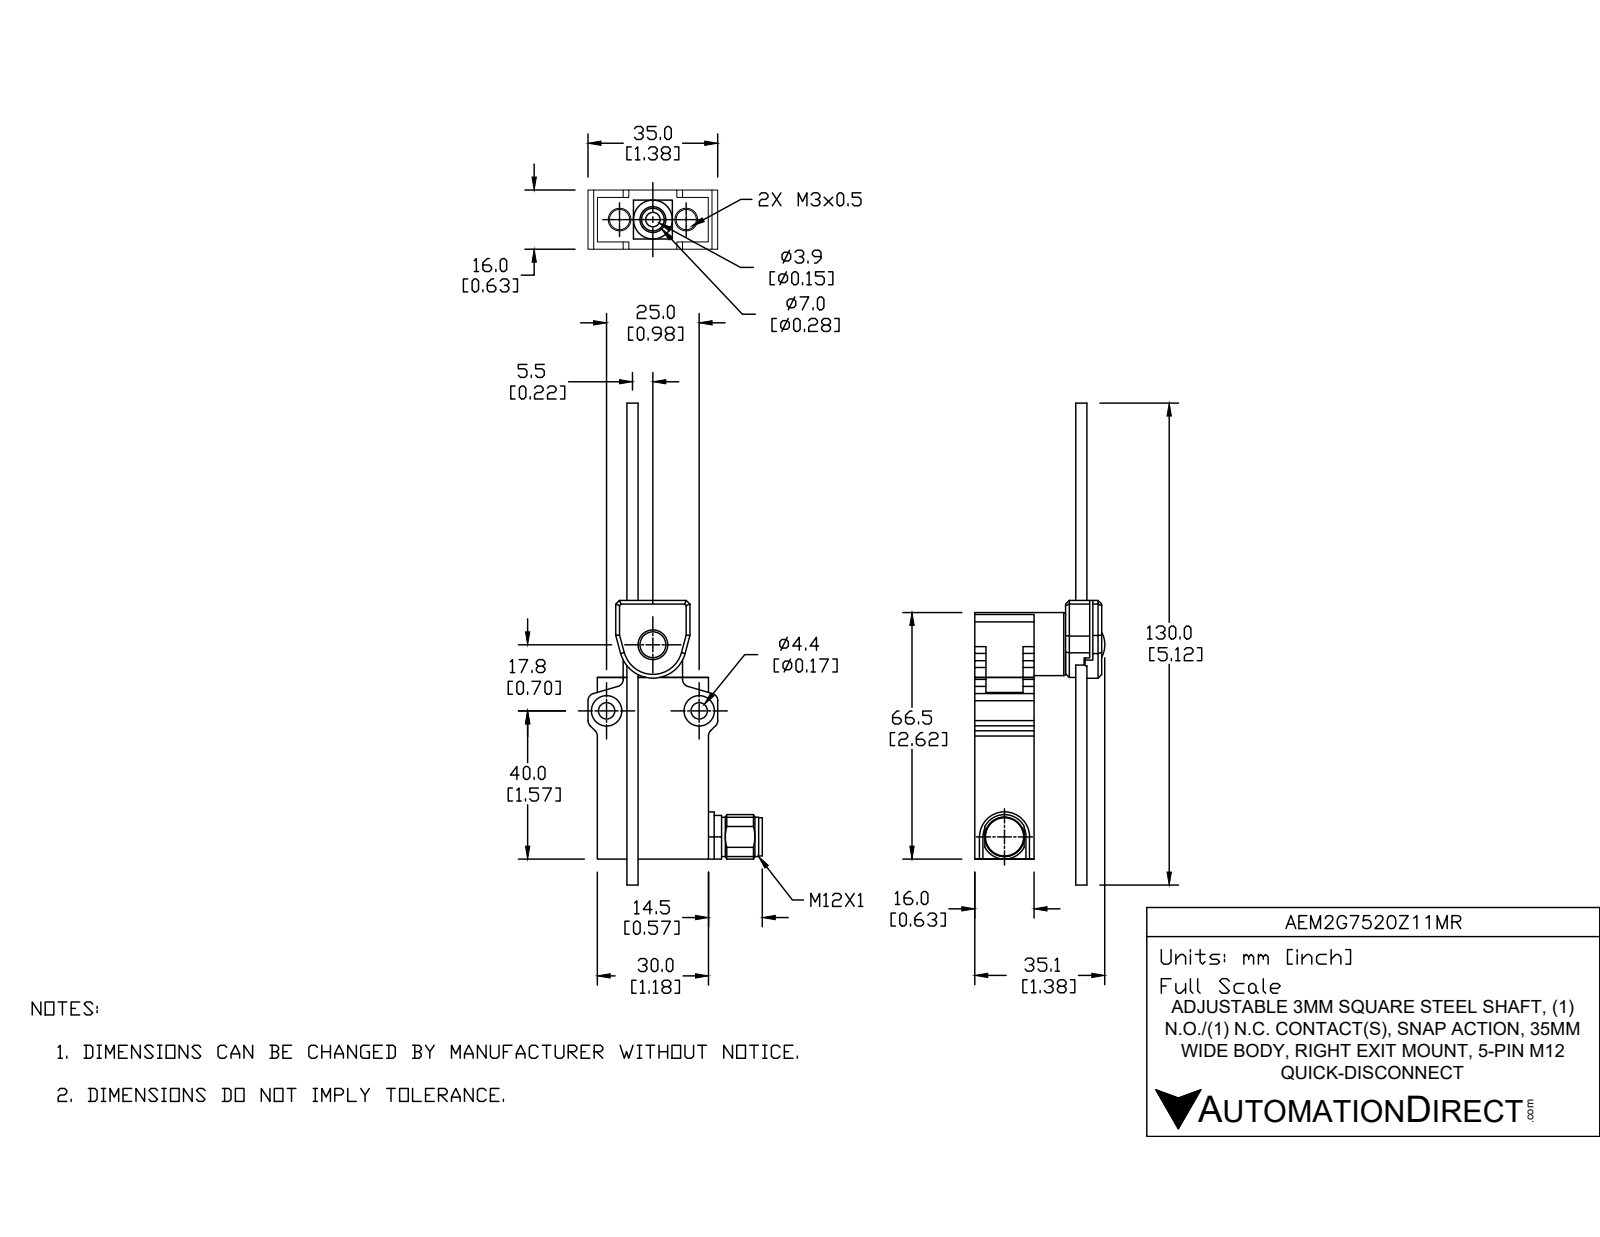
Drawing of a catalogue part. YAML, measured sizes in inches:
part_name: "AEM2G7520Z11MR"
step_written_by: "SolidWorks 2019 (AUTOMOTIVE_DESIGN)"
units: inches
bodies: {solids: 7, faces: 242, planar: 147, cylindrical: 60, other: 35}
overall_size: [6.86, 1.831, 1.366]
volume: 2.105
surface_area: 21.94
round_holes:
  - {diameter: 0.118, count: 2}
  - {diameter: 0.173, count: 2}
  - {diameter: 0.323, count: 2}
  - {diameter: 0.197, count: 1}
  - {diameter: 0.315, count: 1}
round_bosses_or_shafts:
  - {diameter: 0.622, count: 1}
  - {diameter: 0.472, count: 1}
  - {diameter: 0.417, count: 1}
  - {diameter: 0.406, count: 1}
  - {diameter: 0.276, count: 1}
  - {diameter: 0.138, count: 1}
partial_cylinders:
  - {radius: 0.079, count: 8}
  - {radius: 0.059, count: 2}
  - {radius: 0.173, count: 1}
  - {radius: 0.256, count: 1}
  - {radius: 0.26, count: 1}
  - {radius: 0.354, count: 1}
face_to_face_distances: [0.63, 0.118, 1.181, 1.098, 0.587, 0.435, 0.746, 1.217, 0.469, 0.864]
hole_center_spacings: [0.863, 0.748, 0.984]
